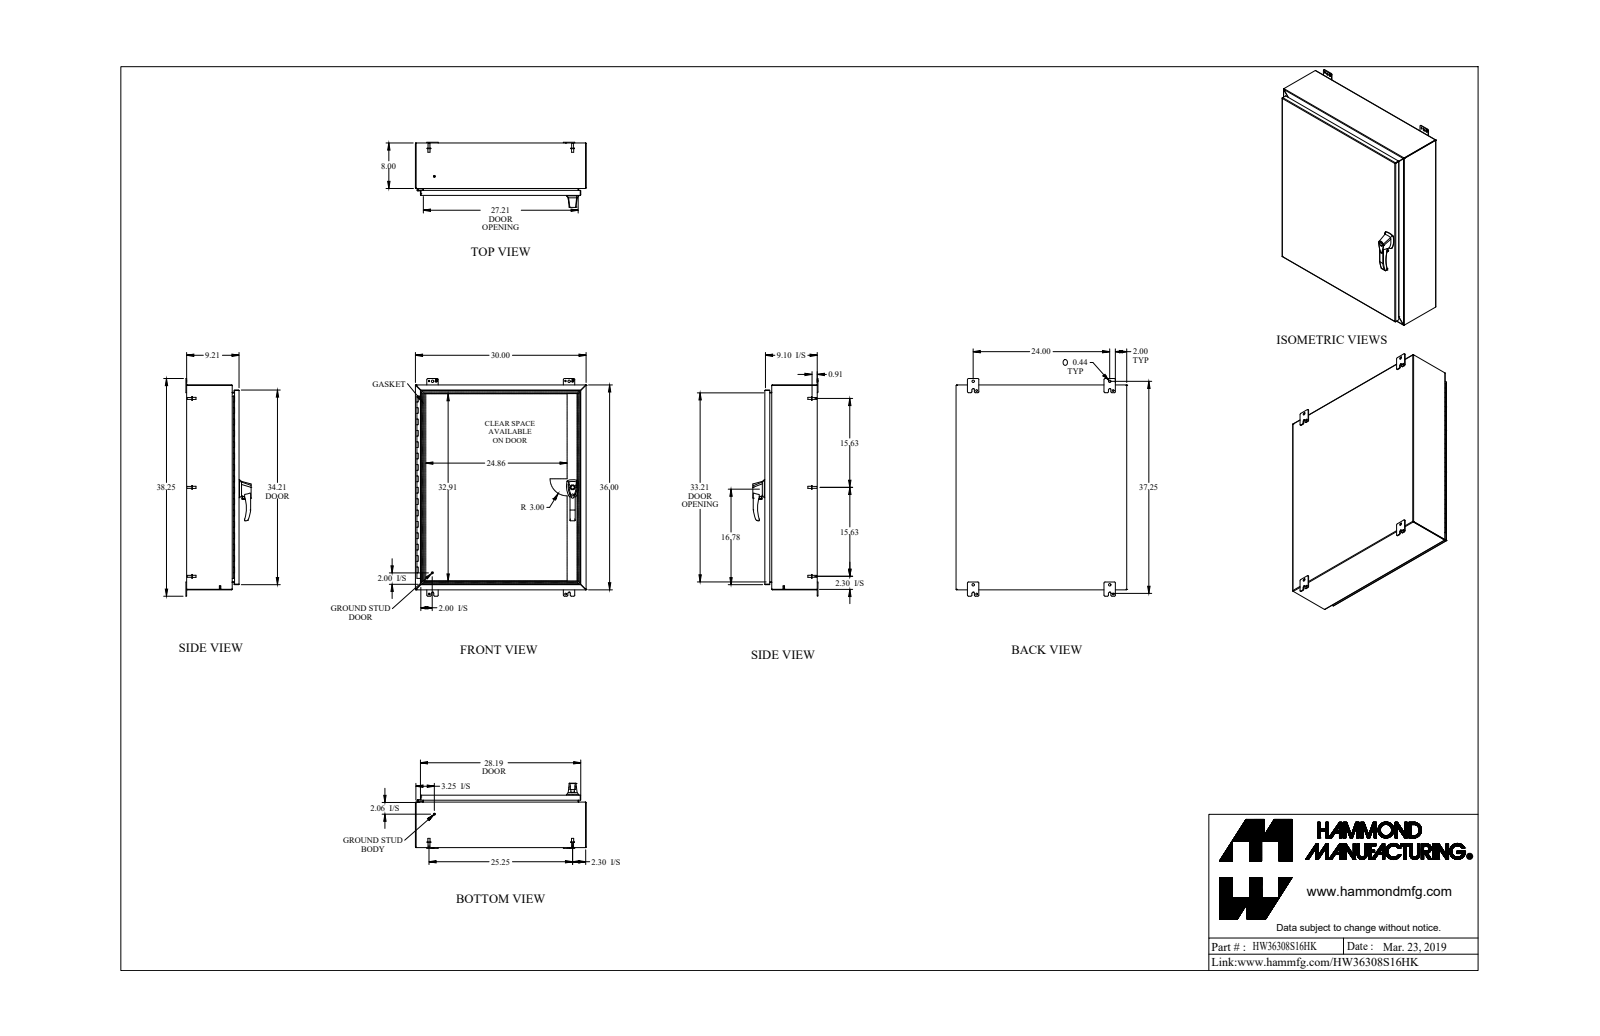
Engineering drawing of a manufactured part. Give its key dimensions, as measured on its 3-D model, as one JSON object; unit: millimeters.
{"part_name": "HW36308S16HK", "step_written_by": "SolidWorks 2018 (AUTOMOTIVE_DESIGN)", "units": "millimeters", "bodies": {"solids": 44, "faces": 1542, "planar": 720, "cylindrical": 658, "other": 164}, "overall_size": [971.6, 762, 290.8], "volume_mm3": 4805000, "surface_area_mm2": 4976000, "round_holes": [[4.5, 6], [8, 5], [6.4, 3], [6.7, 3], [10.5, 3], [5, 2], [6.5, 2], [10, 2], [11.1, 2], [2.8, 1], [5.9, 1], [8.4, 1]], "round_bosses_or_shafts": [[9.5, 11], [6.4, 7], [16.5, 6], [8.4, 6], [4, 6], [8, 4], [25.4, 3], [13, 3]], "partial_cylinders_radius": [[6.4, 27], [4.8, 24], [0.9, 20], [2.7, 20], [1.5, 12], [3.2, 9], [1.1, 8], [5.5, 8]], "face_to_face_distances": [1.8, 232.1, 230.3, 232.1, 233.9, 1.8, 760.2, 912.6, 201.4, 758.3], "hole_center_spacings": [28.2, 358.6, 358.6, 717.2, 34, 324.6, 358.6, 392.6]}
